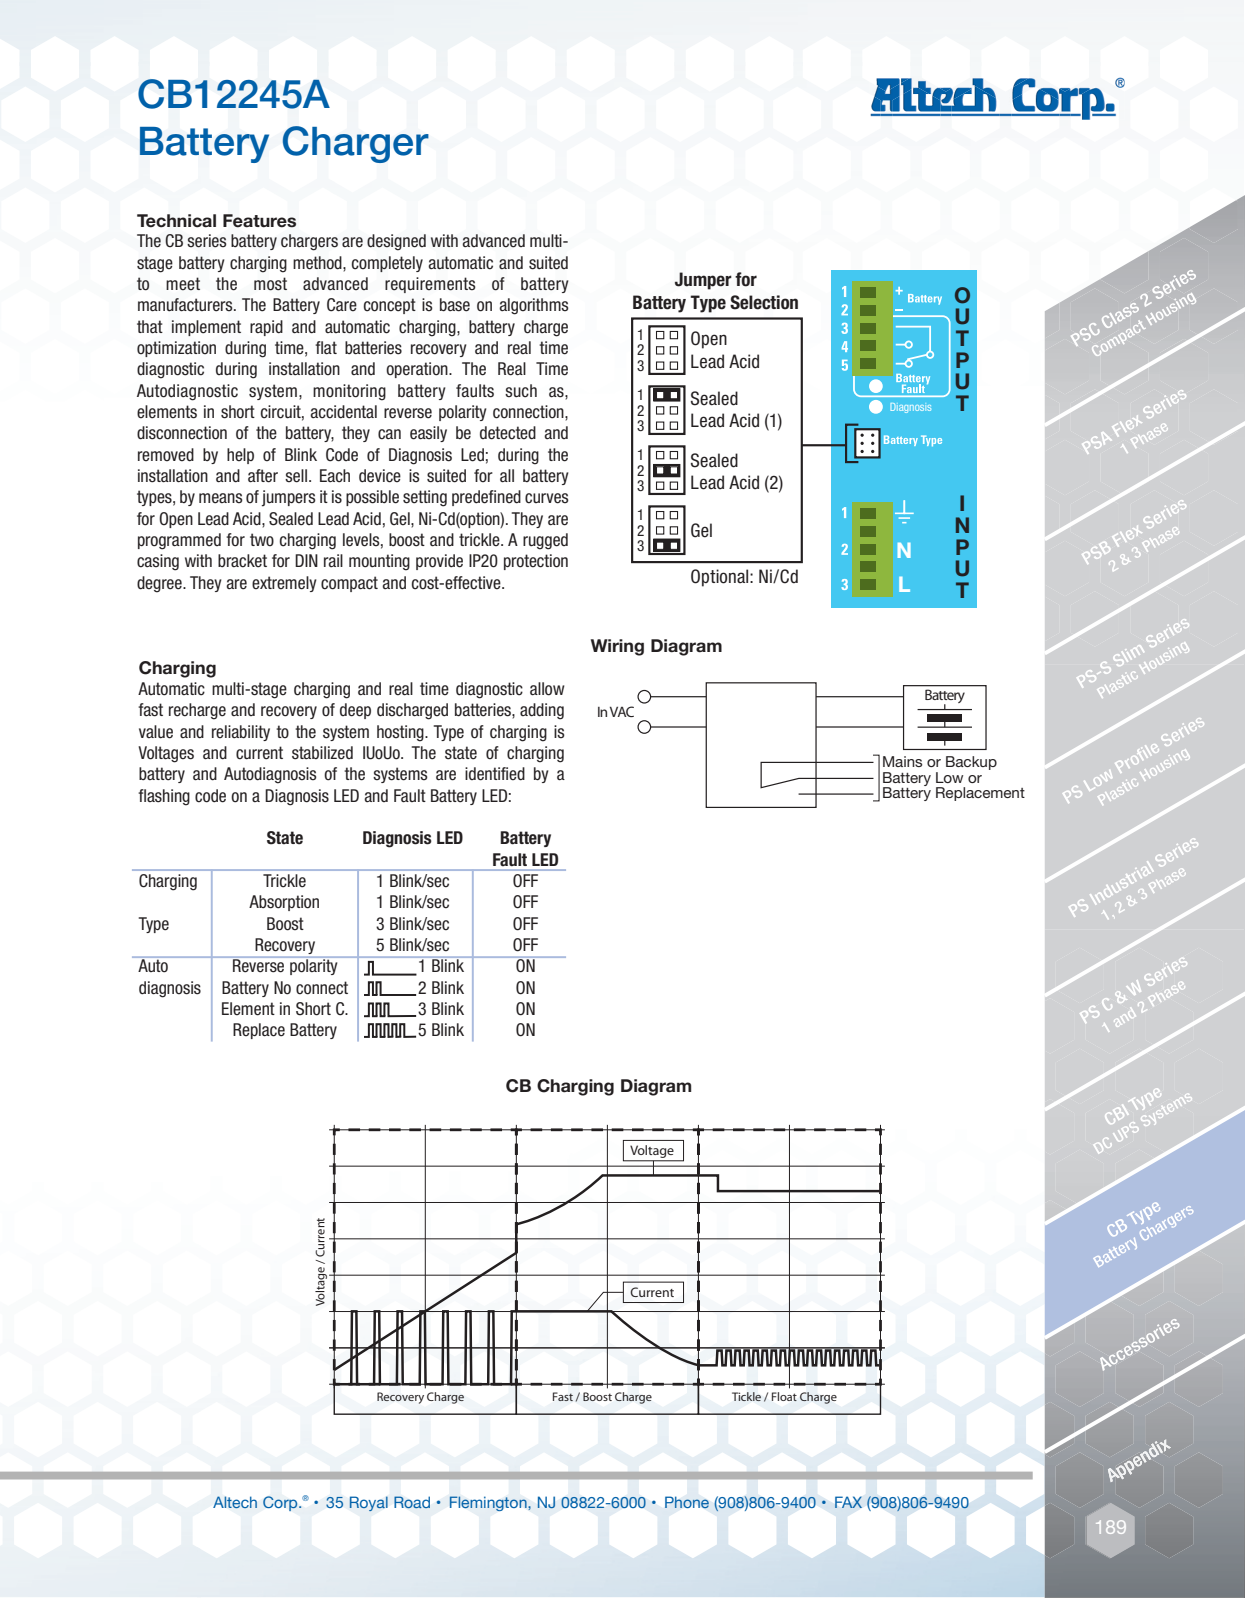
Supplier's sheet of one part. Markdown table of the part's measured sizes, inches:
| quantity | value |
| --- | --- |
| part name | CB12245A; M3M_00F_041_A2_Fondo; SOS-440-4; M3M_00C_041_Coperchio (+8 more) |
| STEP written by | Autodesk Inventor 2024 (AUTOMOTIVE_DESIGN) |
| units | inches |
| bodies | 52 solids, 3647 faces (2118 planar, 1031 cylindrical, 498 other) |
| overall size | 4.508 × 4.339 × 1.874 |
| volume | 4.233 in³ |
| surface area | 173.3 in² |
| round holes (diameter × count) | 0.039 × 102, 0.059 × 5, 0.098 × 2, 0.122 × 2, 0.126 × 2, 0.13 × 2, 0.097 × 1, 0.11 × 1, 0.138 × 1, 0.197 × 1, 0.236 × 1 |
| round bosses / shafts (diameter × count) | 0.108 × 10, 0.118 × 4, 0.105 × 4, 0.094 × 2, 0.354 × 1, 0.236 × 1, 0.22 × 1, 0.197 × 1 |
| partial cylindrical surfaces (radius × count) | 0.005 × 169, 0.004 × 37, 0.008 × 32, 0.01 × 25, 0.022 × 24, 0.394 × 16, 0.059 × 14, 0.069 × 10 |
| main face-to-face distances | 0.059, 0.039, 1.724, 1.665, 1.764, 1.705, 0.256, 1.346, 1.386, 0.378 |
| hole center spacings | 0.2, 1, 1.02, 1.077, 0.4, 0.6, 1.166, 0.8 |
